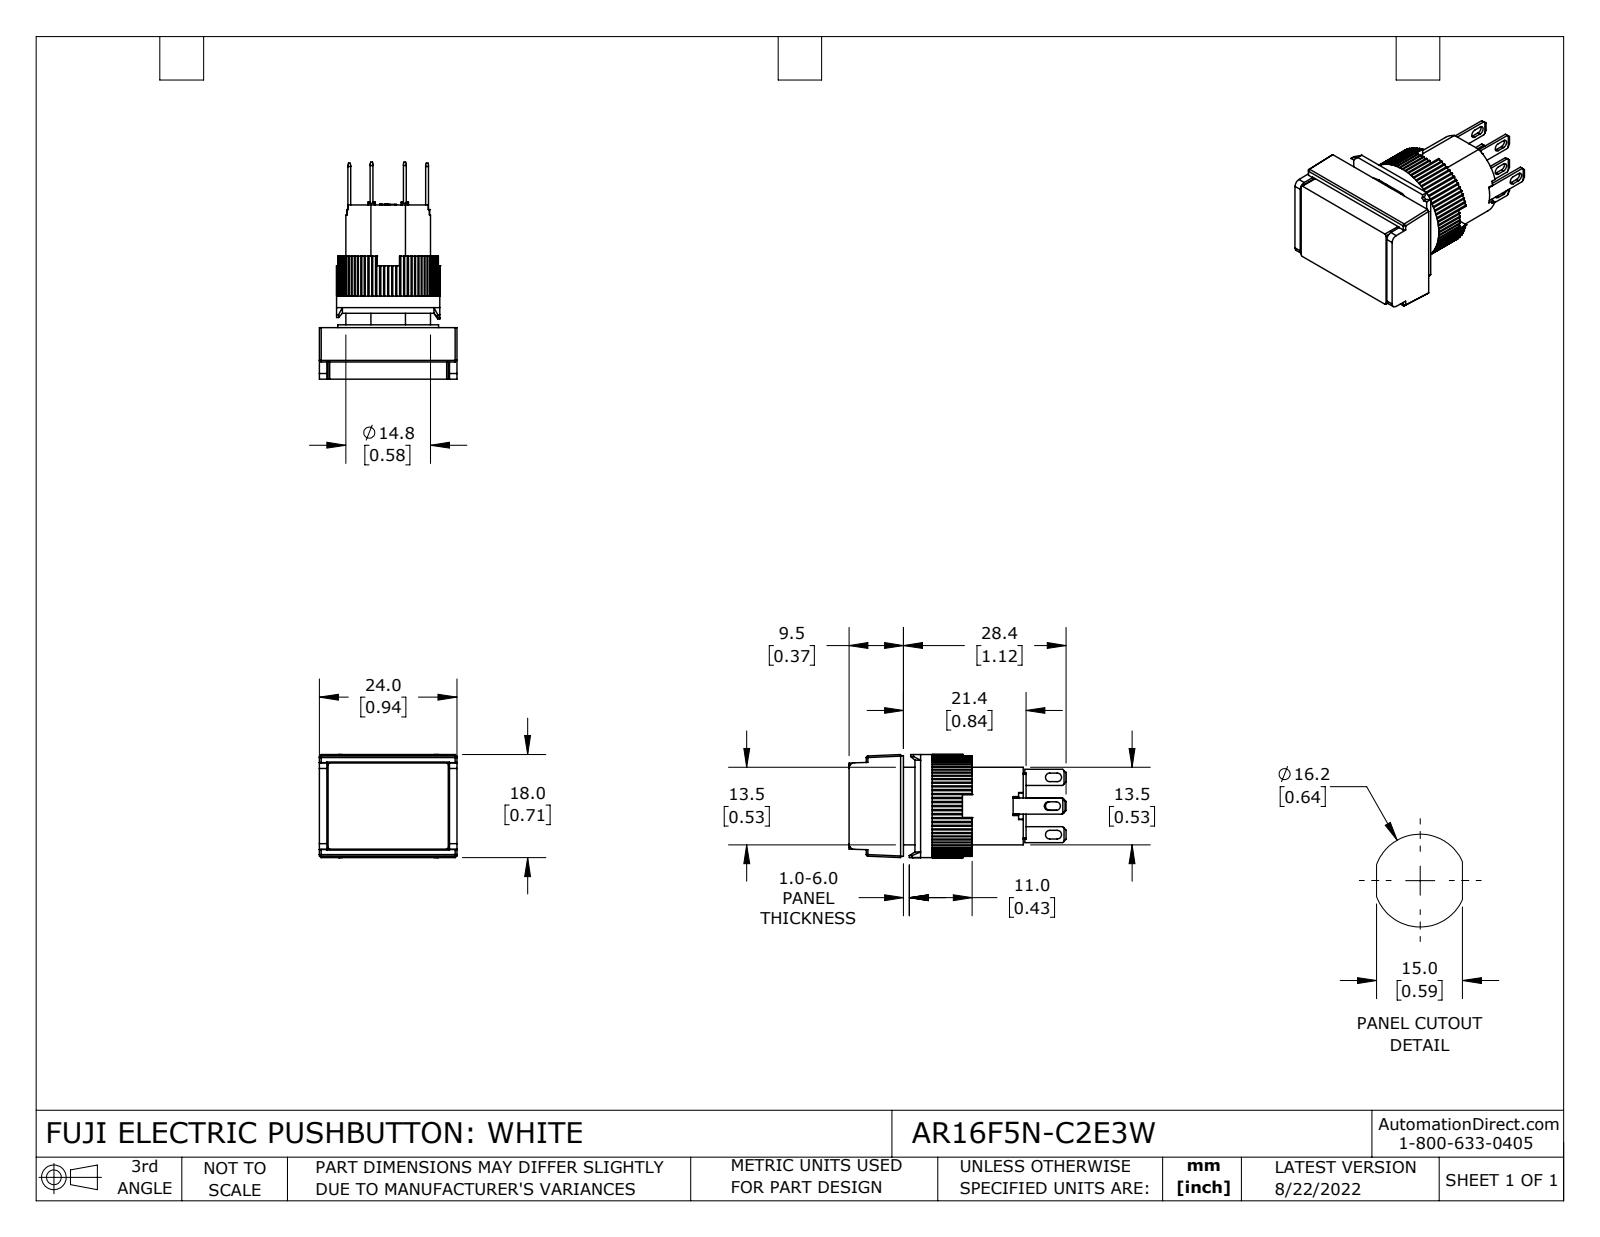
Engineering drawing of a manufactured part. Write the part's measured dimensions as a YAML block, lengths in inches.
part_name: "AR16F5N-C2E3W"
step_written_by: "SolidWorks 2021 (CONFIG_CONTROL_DESIGN)"
units: inches
bodies: {solids: 14, faces: 843, planar: 656, cylindrical: 183, other: 4}
overall_size: [1.492, 0.945, 0.709]
volume: 0.444
surface_area: 9.306
round_holes:
  - {diameter: 0.543, count: 1}
  - {diameter: 0.583, count: 1}
round_bosses_or_shafts:
  - {diameter: 0.709, count: 1}
  - {diameter: 0.693, count: 1}
partial_cylinders:
  - {radius: 0.01, count: 80}
  - {radius: 0.008, count: 12}
  - {radius: 0.03, count: 8}
  - {radius: 0.012, count: 6}
  - {radius: 0.039, count: 2}
face_to_face_distances: [0.213, 0.354, 0.142, 0.35, 0.492, 0.138, 0.02, 0.843, 0.059, 0.453]
